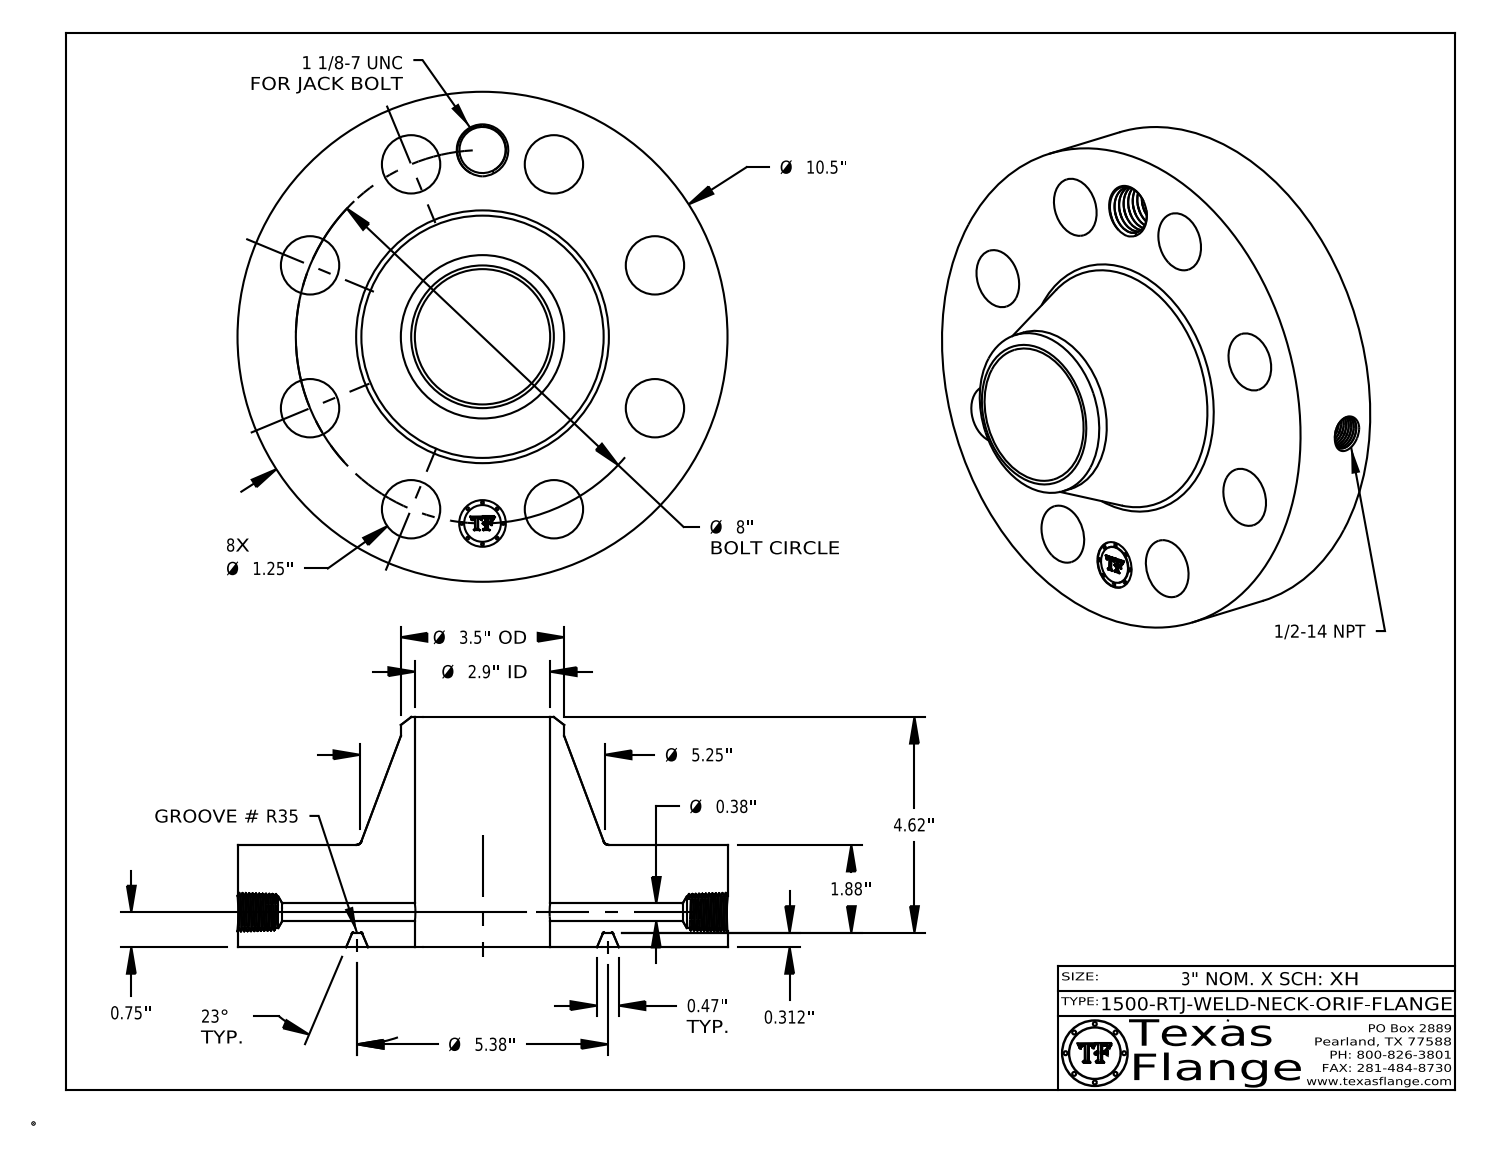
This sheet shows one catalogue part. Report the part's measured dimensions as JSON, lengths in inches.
{"part_name": "1500-RTJ-WELD-NECK", "step_written_by": "CATIA V5 STEP AP214 (AUTOMOTIVE_DESIGN)", "units": "inches", "bodies": {"solids": 1, "faces": 779, "planar": 370, "cylindrical": 92, "other": 317}, "overall_size": [10.5, 10.5, 4.932], "volume_in3": 169.9, "surface_area_in2": 380.2, "round_holes": [[1.25, 8], [0.375, 1], [0.672, 1], [0.984, 1], [1, 1], [2.9, 1]], "round_bosses_or_shafts": [[0.061, 8], [10.5, 1], [3.5, 1], [0.788, 1]], "face_to_face_distances": [2.192, 0.312, 1.88, 4.932, 4.62, 2.74, 2.177, 1.865, 0.015, 2.755], "hole_center_spacings": [4, 5.657, 7.391, 1.561, 3.061, 3.062, 4.445, 6.652]}
